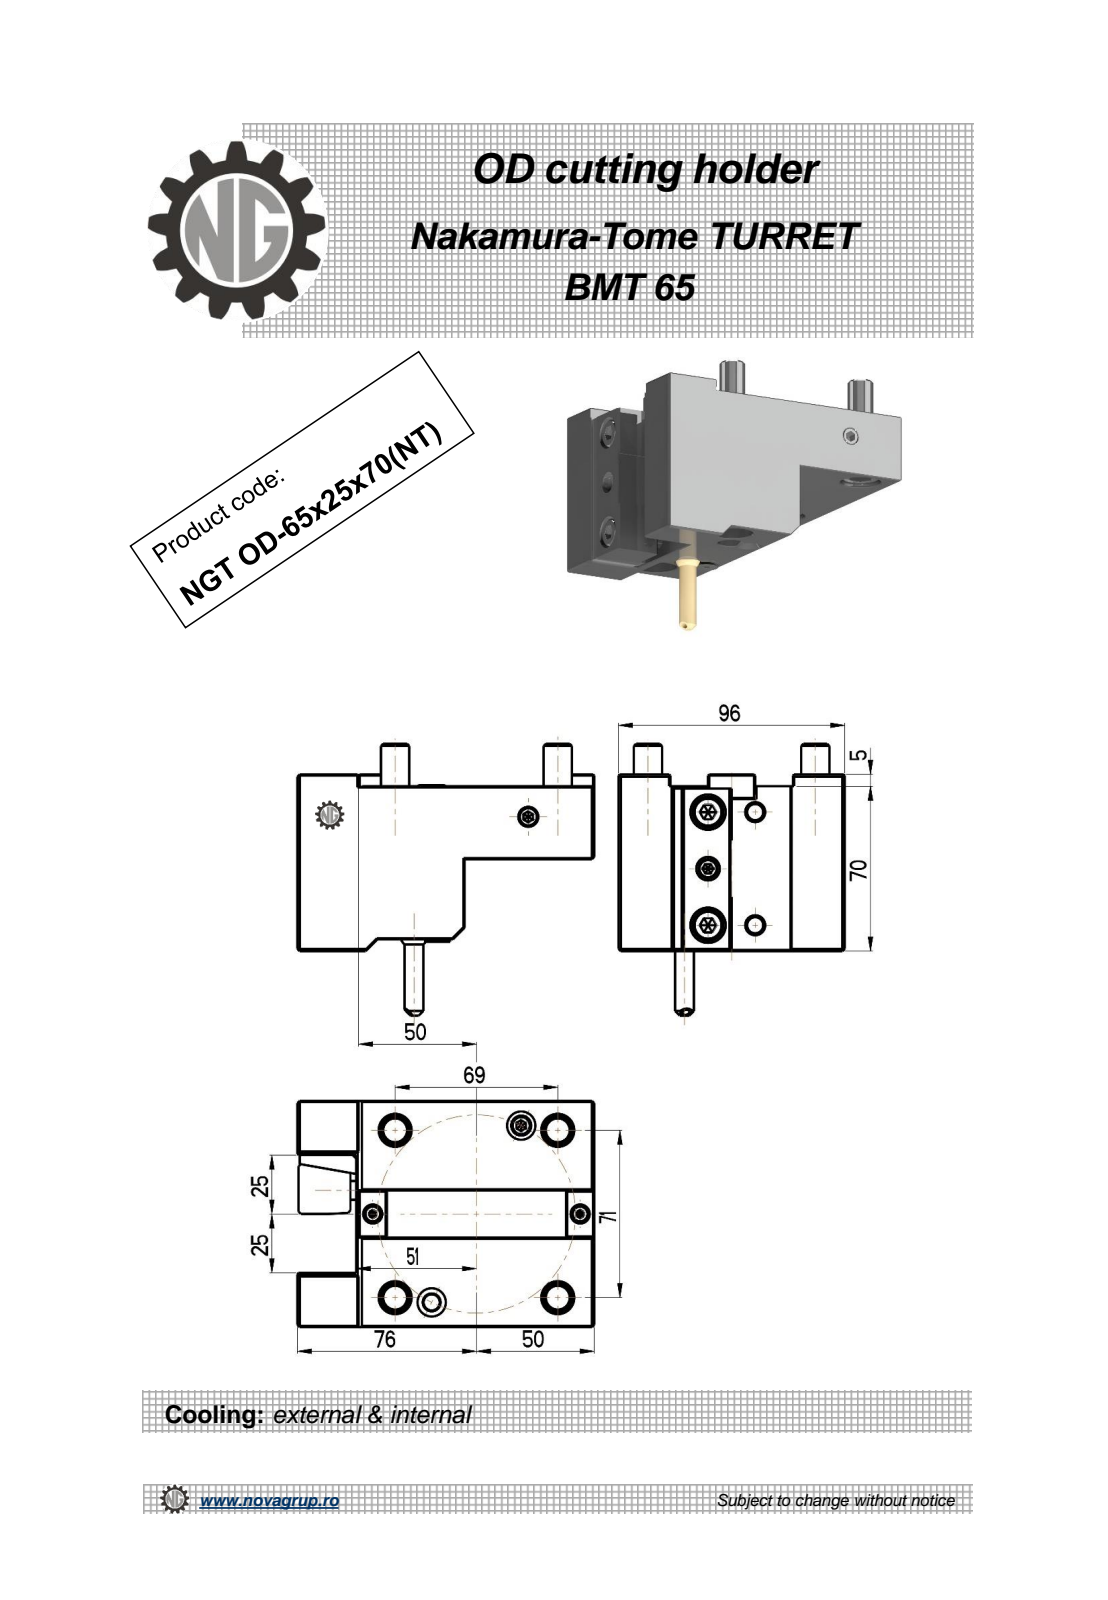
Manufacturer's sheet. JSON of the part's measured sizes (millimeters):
{"part_name": "NGT_OD_65_25_70_NT", "step_written_by": "PRO/ENGINEER BY PARAMETRIC TECHNOLOGY CORPORATION, 2010280 (CONFIG_CONTROL_DESIGN)", "units": "millimeters", "bodies": {"solids": 1, "faces": 211, "planar": 135, "cylindrical": 43, "other": 33}, "overall_size": [126, 115.34, 96], "volume_mm3": 579789, "surface_area_mm2": 61420, "round_holes": [[12, 2], [3, 1], [5, 1], [6.8, 1]], "round_bosses_or_shafts": [[12, 4], [8, 4], [11.2, 1]], "partial_cylinders_radius": [[0.22, 6], [0.41, 6], [1, 1]], "face_to_face_distances": [96, 31, 5, 65, 25, 70, 34, 126, 71, 101], "hole_center_spacings": [48.75, 57.99, 84.08]}
